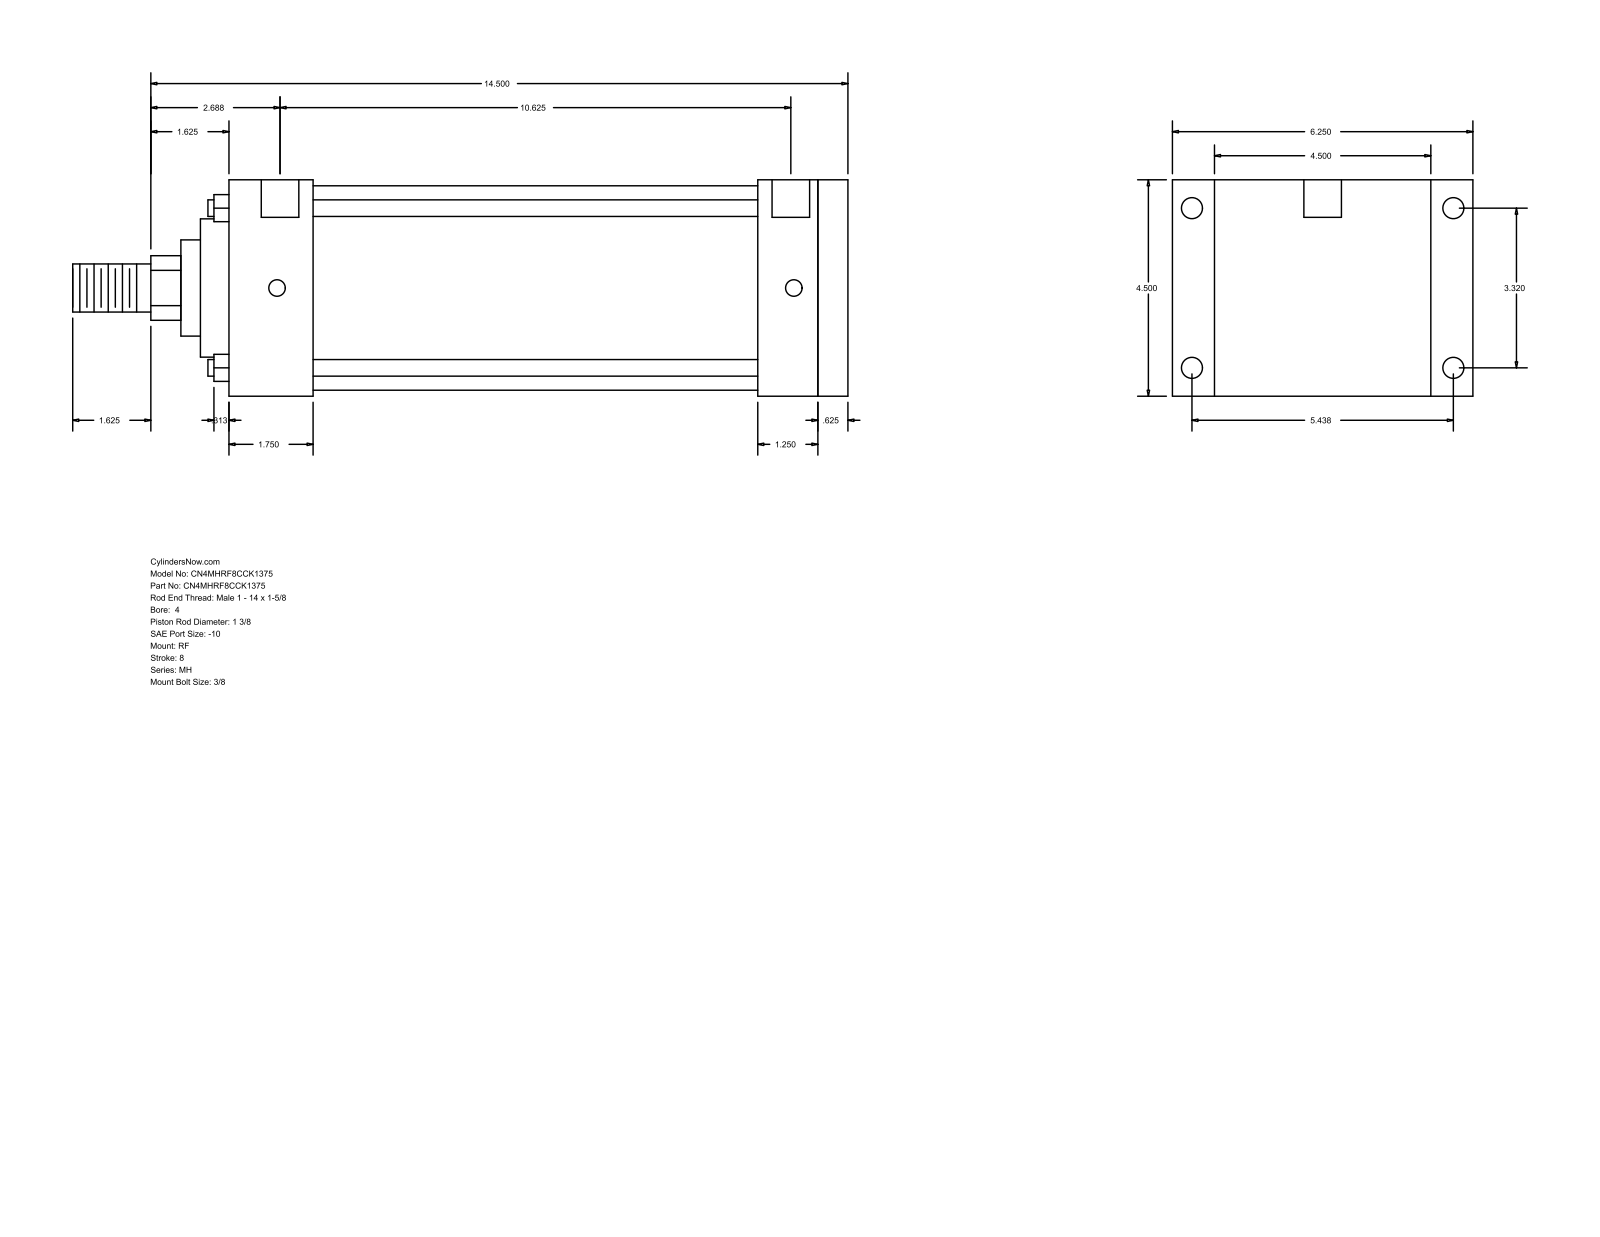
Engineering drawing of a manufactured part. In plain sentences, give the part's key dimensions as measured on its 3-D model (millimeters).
The part is named "MH_RF__0400_1.375". Its 3-D file was written by "GSSL Pune (CONFIG_CONTROL_DESIGN)". It is 0 solids with 94 faces: 65 planar, 29 cylindrical and 0 other. Overall it measures 409.57 by 158.75 by 114.3 millimeters. Round holes: 4 of diameter 8.73, 4 of diameter 11.13, 2 of diameter 19.84. Round bosses or shafts: 4 of diameter 8.76, 1 of diameter 107.95, 1 of diameter 73.03, 1 of diameter 50.8, 1 of diameter 34.92, 1 of diameter 25.4. Partial cylindrical surfaces (rounded edges, fillets, slot ends): 1 of radius 17.06. The main face-to-face distances are 114.3, 327.03, 311.16, 15.87, 44.45, 266.71, 282.58, 279.41, 234.96, 31.75. The hole center spacings are 1.59, 84.32, 138.12, 161.82, 271.47, 273.06, 269.88.
